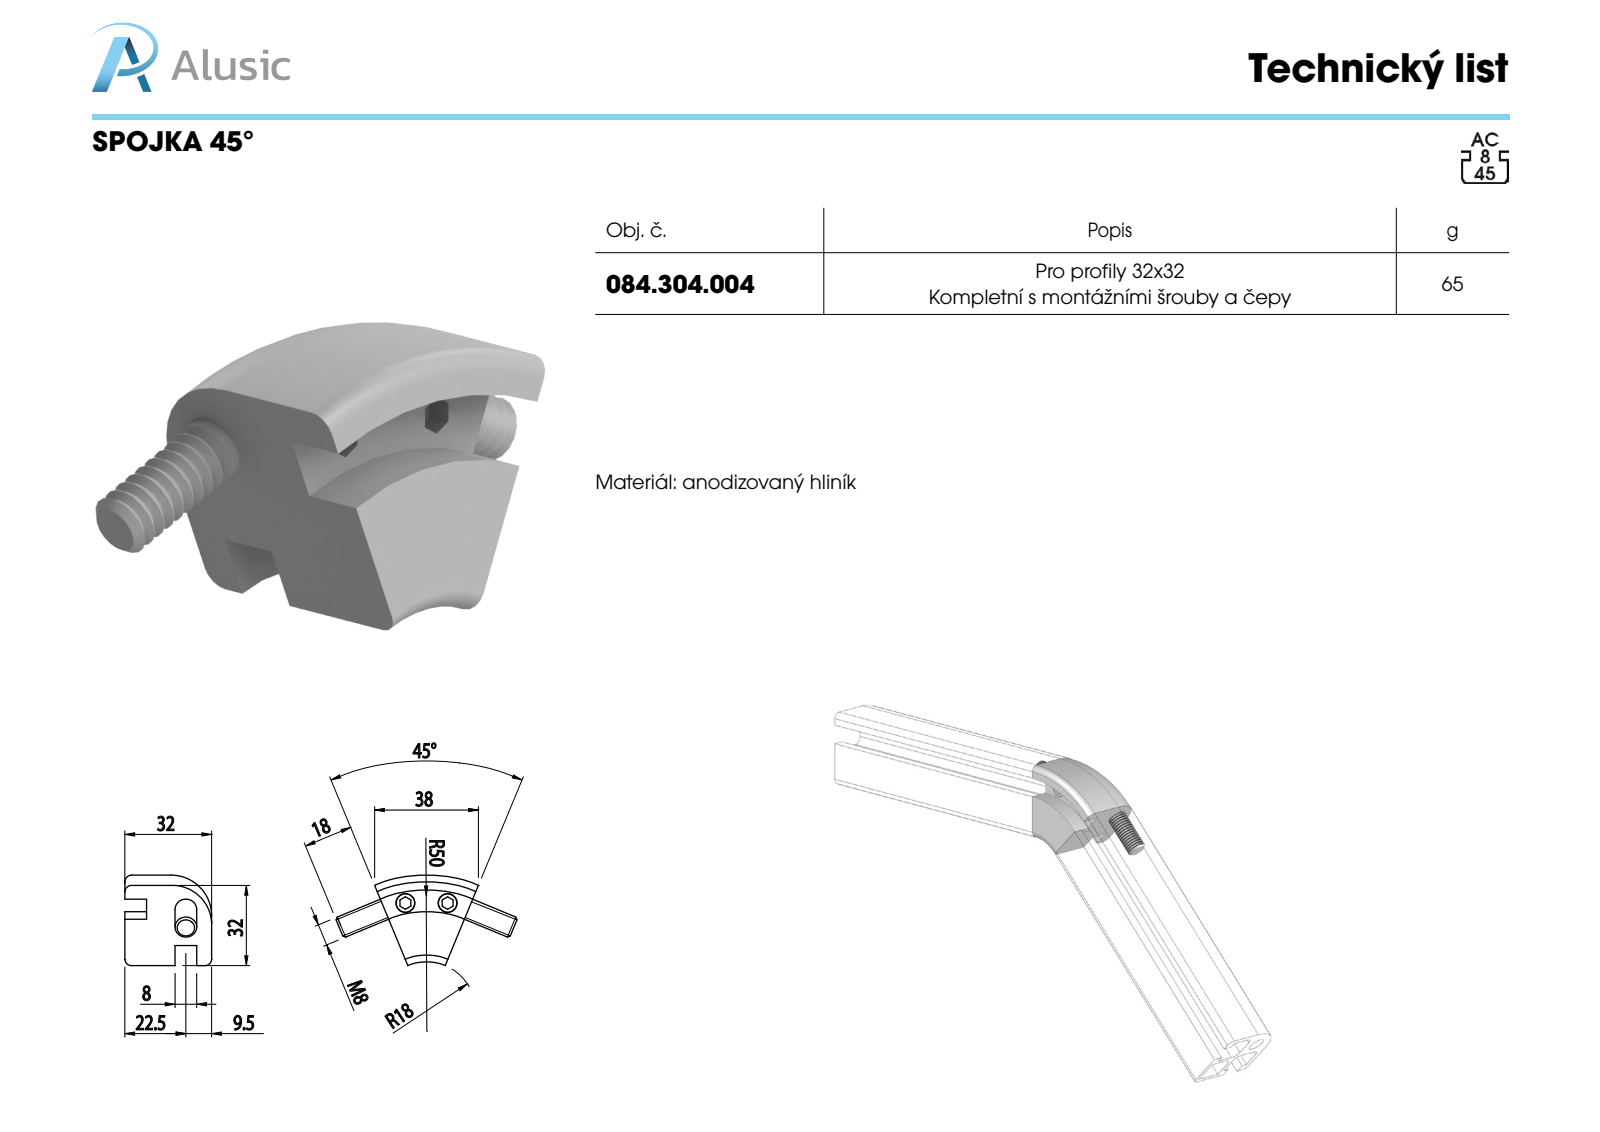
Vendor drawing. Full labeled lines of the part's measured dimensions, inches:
Part name (STEP PRODUCT): 084.304.004
STEP written by: SolidWorks 2011 (CONFIG_CONTROL_DESIGN)
Units: inches
Bodies: 1 solid, 32 faces (8 planar, 14 cylindrical, 10 other)
Overall size (bounding box): 1.507 × 1.314 × 1.26
Volume: 1.224 in³ · Surface area: 10.32 in²
Round holes (diameter × count): ⌀0.268 ×2, ⌀0.315 ×2
Partial cylindrical surfaces — rounded edges, fillets, slot ends (radius × count): R0.709 ×1, R1.024 ×1, R1.437 ×1, R1.752 ×1, R1.969 ×1
Main face-to-face distances: 0.315, 1.26, 0.728, 0.945, 0.217, 1.043, 0.531, 0.413
Hole centre spacings: 0.613
